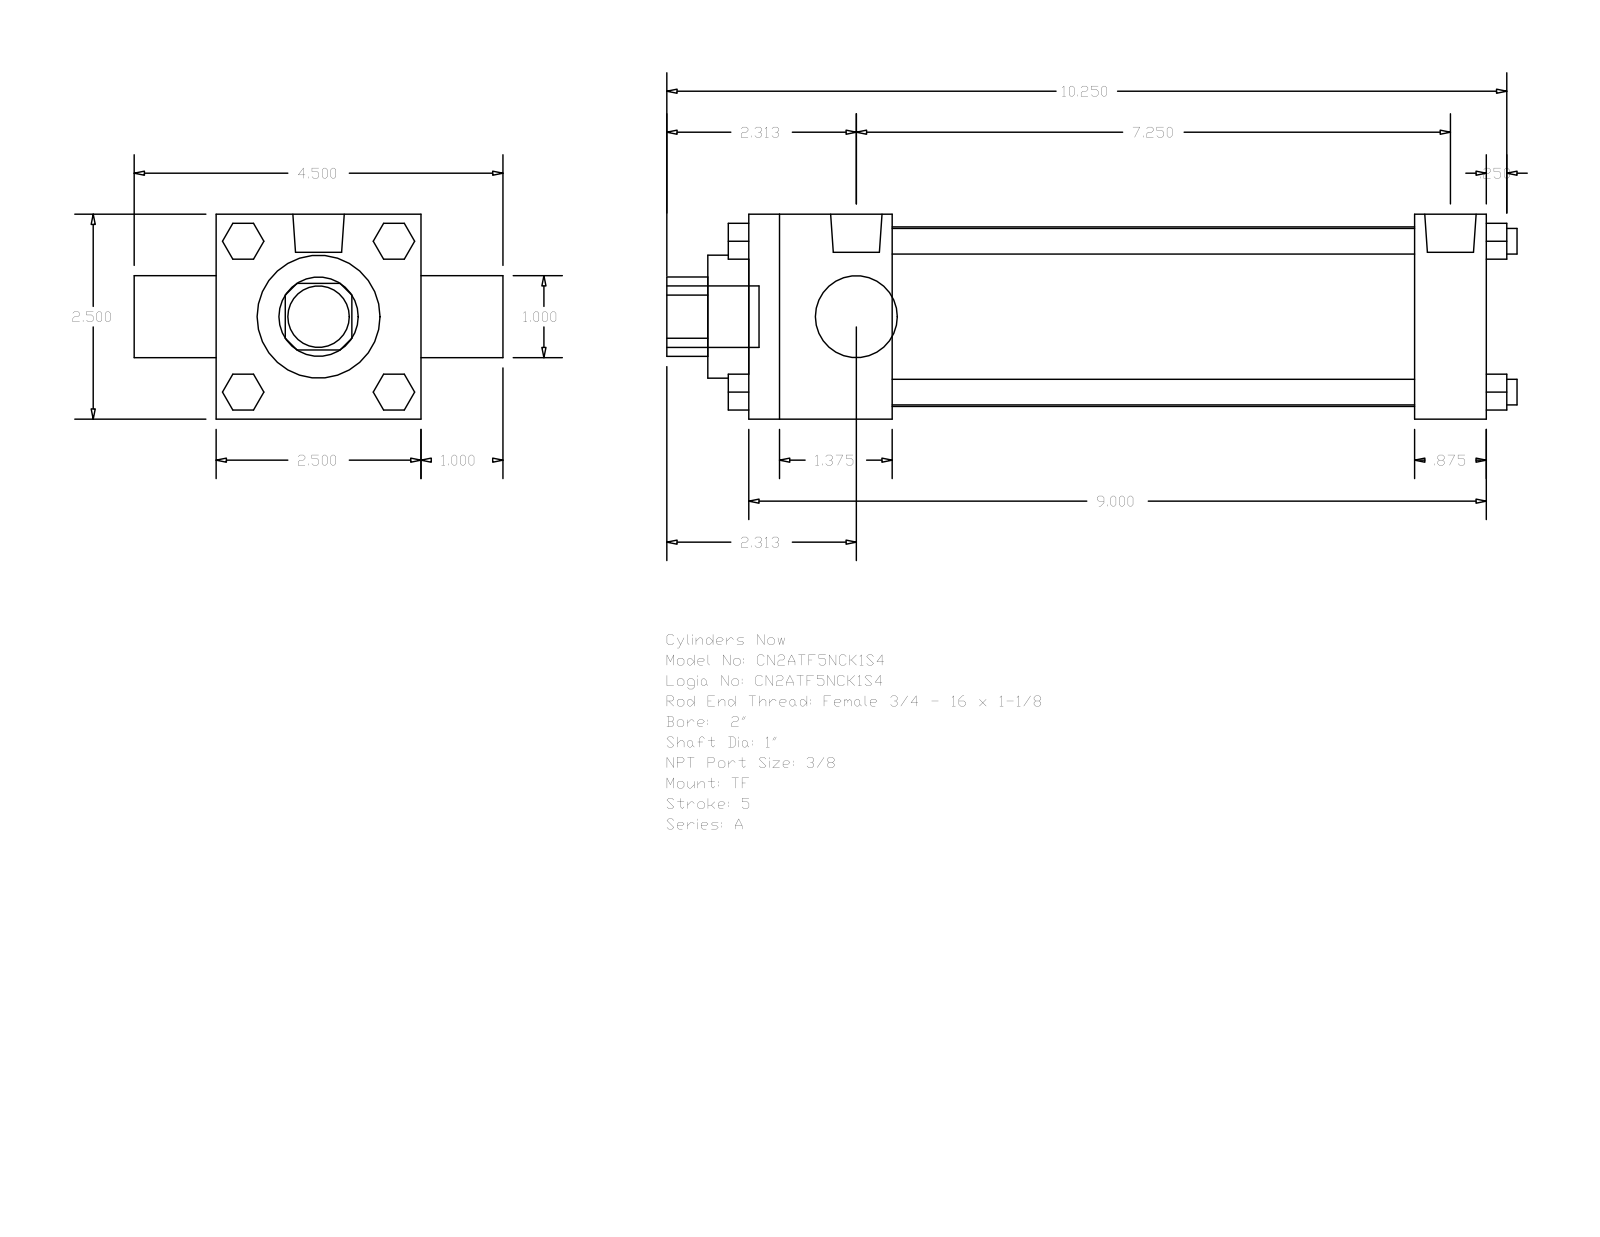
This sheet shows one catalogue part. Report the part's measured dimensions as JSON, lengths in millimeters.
{"part_name": "A_TF__0200_1", "step_written_by": "GSSL Pune (CONFIG_CONTROL_DESIGN)", "units": "millimeters", "bodies": {"solids": 0, "faces": 120, "planar": 92, "cylindrical": 28, "other": 0}, "overall_size": [263.52, 114.3, 63.5], "round_holes": [[25.4, 2], [38.1, 1], [55.63, 1]], "round_bosses_or_shafts": [[7.94, 4], [5.56, 3], [15.93, 2], [19.05, 1]], "partial_cylinders_radius": [[12.29, 1]], "face_to_face_distances": [63.5, 228.6, 44.45, 206.38, 161.93, 184.15, 22.22, 25.4, 88.9, 241.3]}
